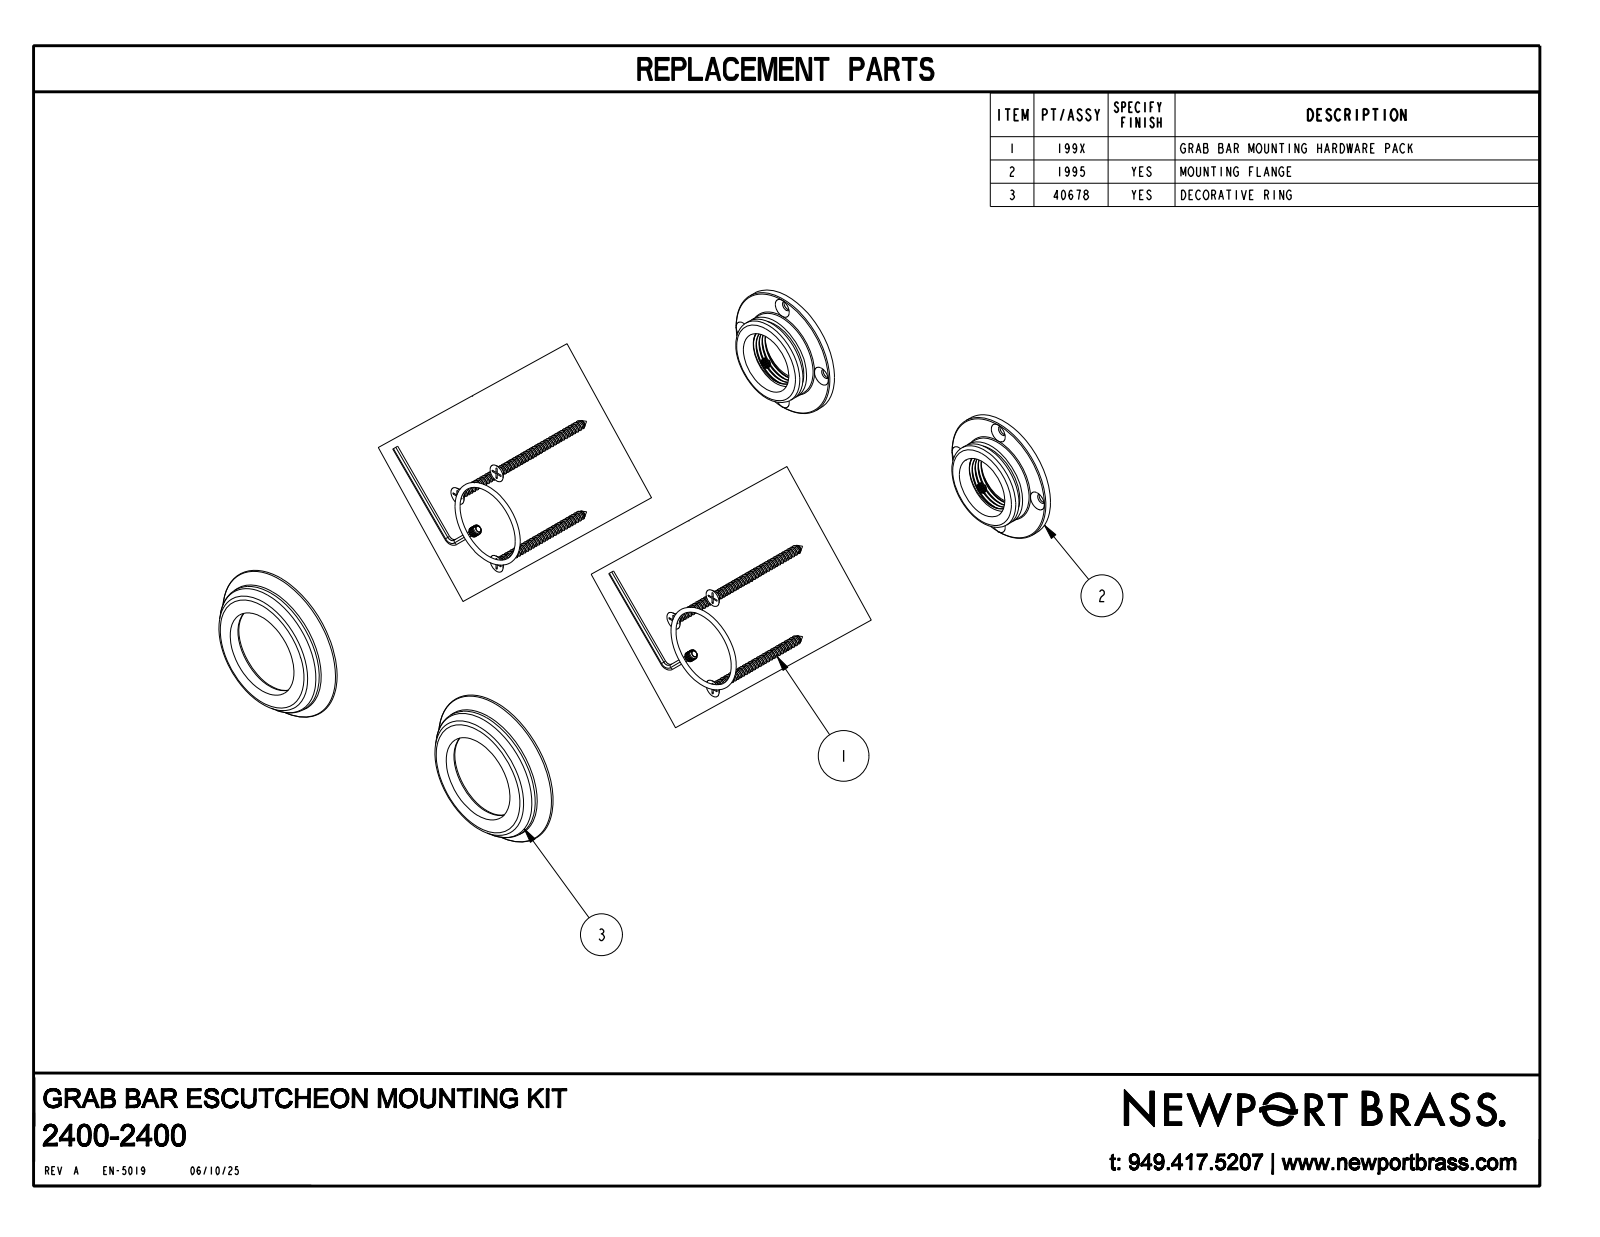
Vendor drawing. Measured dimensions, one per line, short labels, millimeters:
name: 1995; 40678; 2400-2400_ASM
written by: CREO PARAMETRIC BY PTC INC, 2019352 (CONFIG_CONTROL_DESIGN)
unit: mm
bodies: 4 solids, 330 faces (28 planar, 112 cylindrical, 190 other)
size: 232.5 × 80.1 × 15.2
volume: 70 140 mm³; area: 54 880 mm²
holes: 8× ⌀5.1, 2× ⌀4.1, 2× ⌀29.5, 2× ⌀32, 2× ⌀45
bosses: 2× ⌀66, 2× ⌀44.5, 2× ⌀40.5, 2× ⌀5
rounds: 8× R5.4
face distances: 13.3, 2.5, 6.4, 3.8, 7, 9.5, 11.4, 8.9, 15.2, 1.9
hole spacings: 27.6, 39.1, 152.4, 55.2, 127.8, 154.9, 182.1, 124.8
